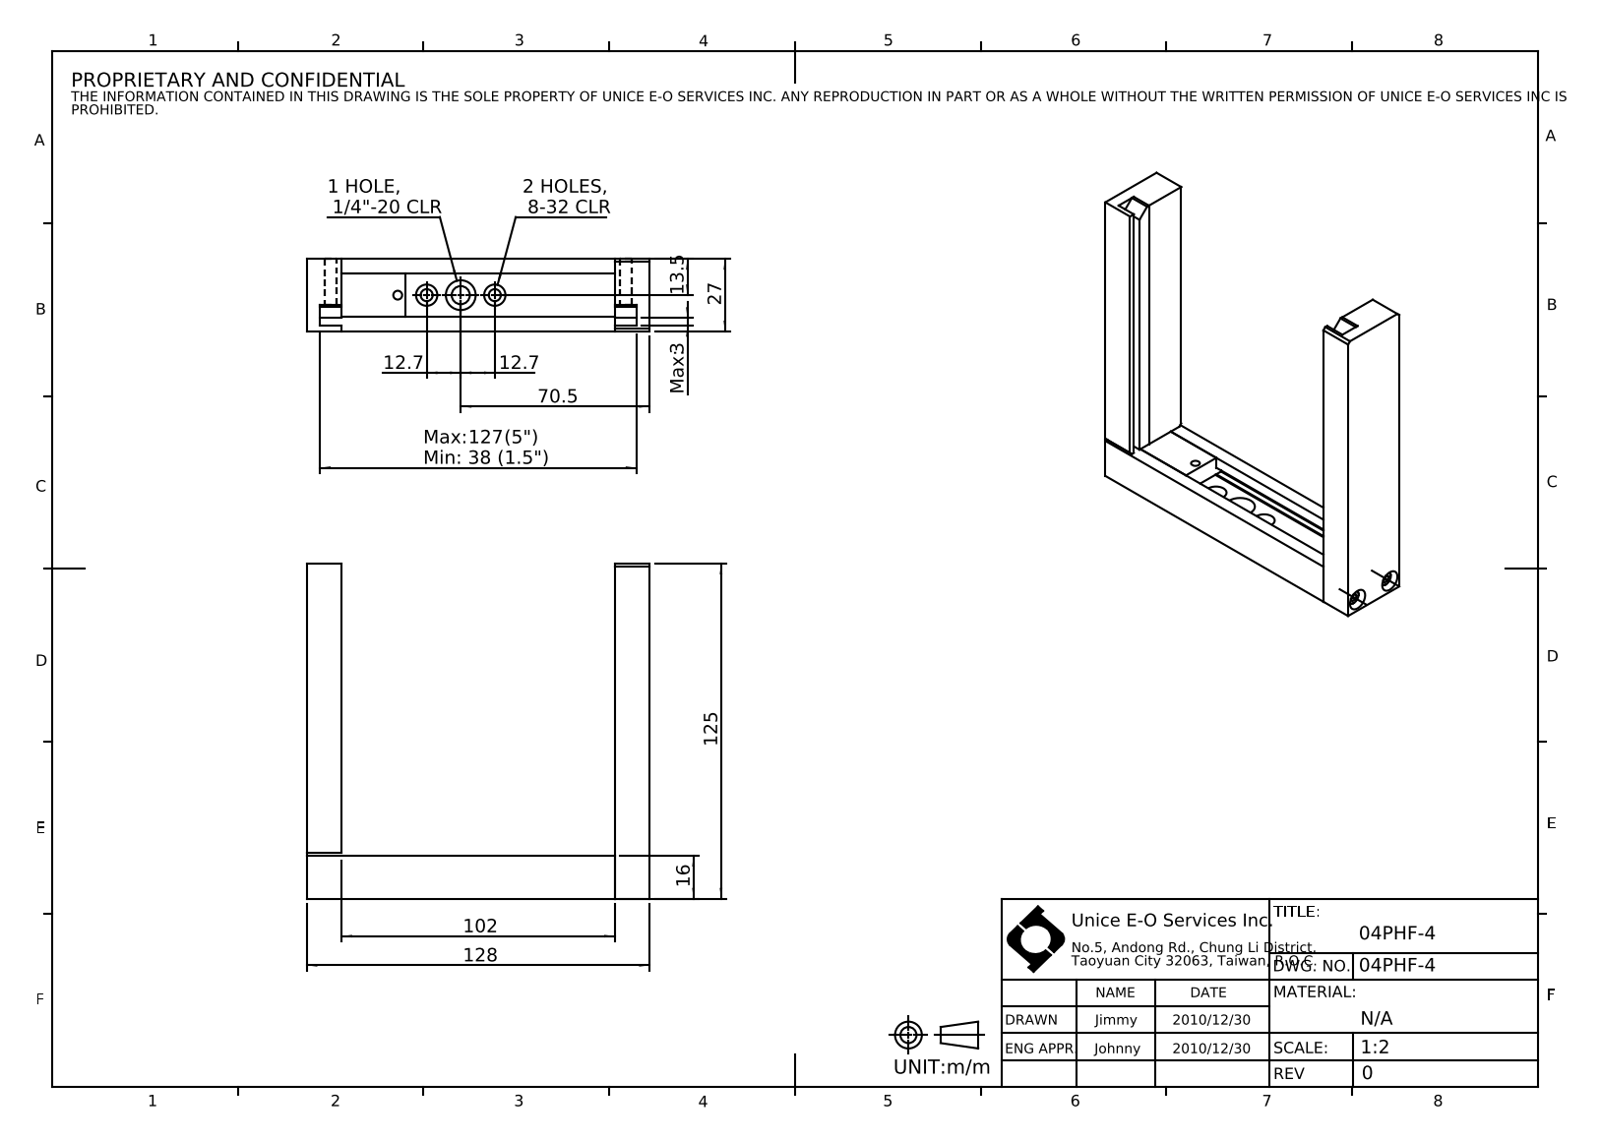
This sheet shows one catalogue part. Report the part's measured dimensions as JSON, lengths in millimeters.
{"part_name": "04PHF-4", "step_written_by": "SolidWorks 2016 (CONFIG_CONTROL_DESIGN)", "units": "millimeters", "bodies": {"solids": 20, "faces": 297, "planar": 169, "cylindrical": 102, "other": 26}, "overall_size": [128, 125, 27], "volume_mm3": 112069, "surface_area_mm2": 50156, "round_holes": [[3.6, 6], [4, 6], [4.2, 6], [3.3, 4], [4.5, 3], [8, 3], [4.5, 2], [7.94, 2], [6.76, 1], [11.11, 1]], "round_bosses_or_shafts": [[5, 6], [5.5, 2], [3, 2]], "partial_cylinders_radius": [[4, 1]], "face_to_face_distances": [8, 5, 13, 115, 27, 17, 3, 10, 128, 16], "hole_center_spacings": [35.5, 115.59, 110, 12.7, 71, 130.92, 10.8, 17]}
